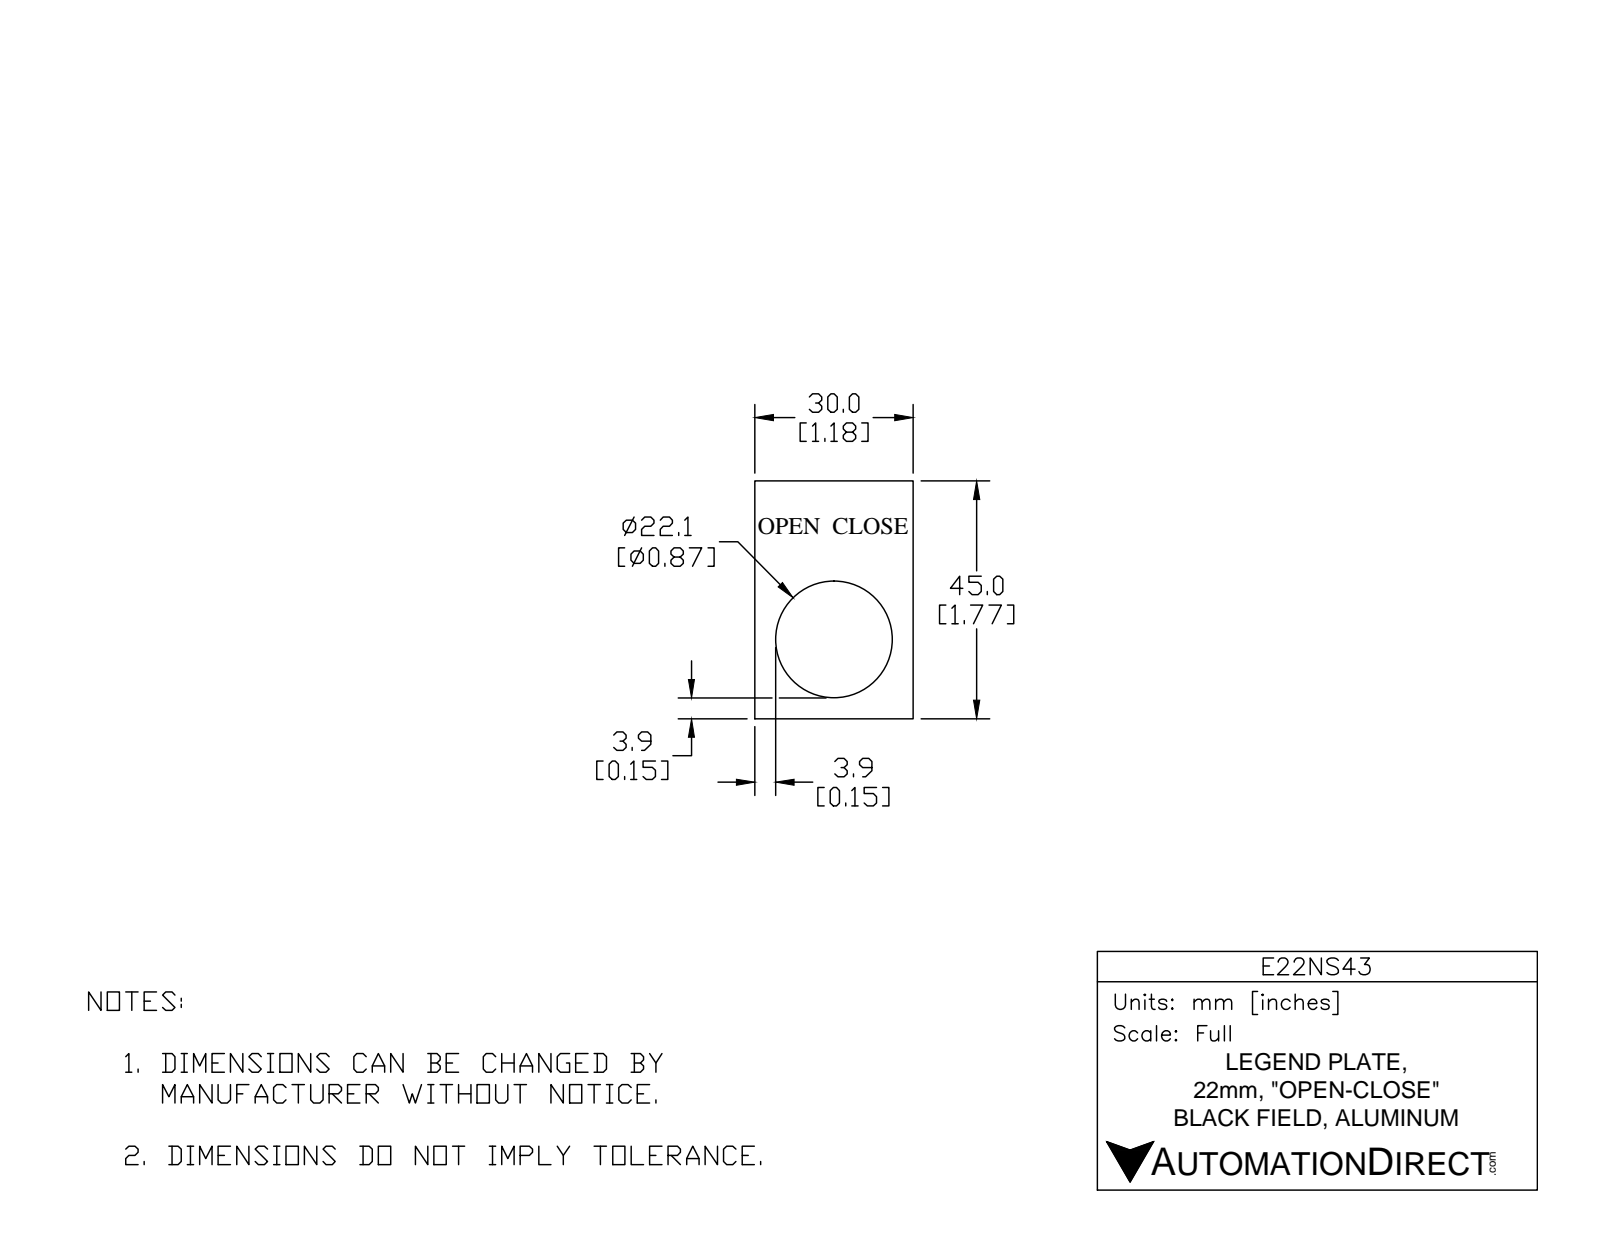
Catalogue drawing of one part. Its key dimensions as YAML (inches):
part_name: "E22NS43"
step_written_by: "SolidWorks 2017 (AUTOMOTIVE_DESIGN)"
units: inches
bodies: {solids: 1, faces: 127, planar: 78, cylindrical: 3, other: 46}
overall_size: [1.772, 1.181, 0.051]
volume: 0.076
surface_area: 3.494
round_holes:
  - {diameter: 0.874, count: 1}
face_to_face_distances: [0.051, 1.181, 1.772, 0.041, 0.185, 1.587, 0.528, 0.013, 0.654, 0.126]
